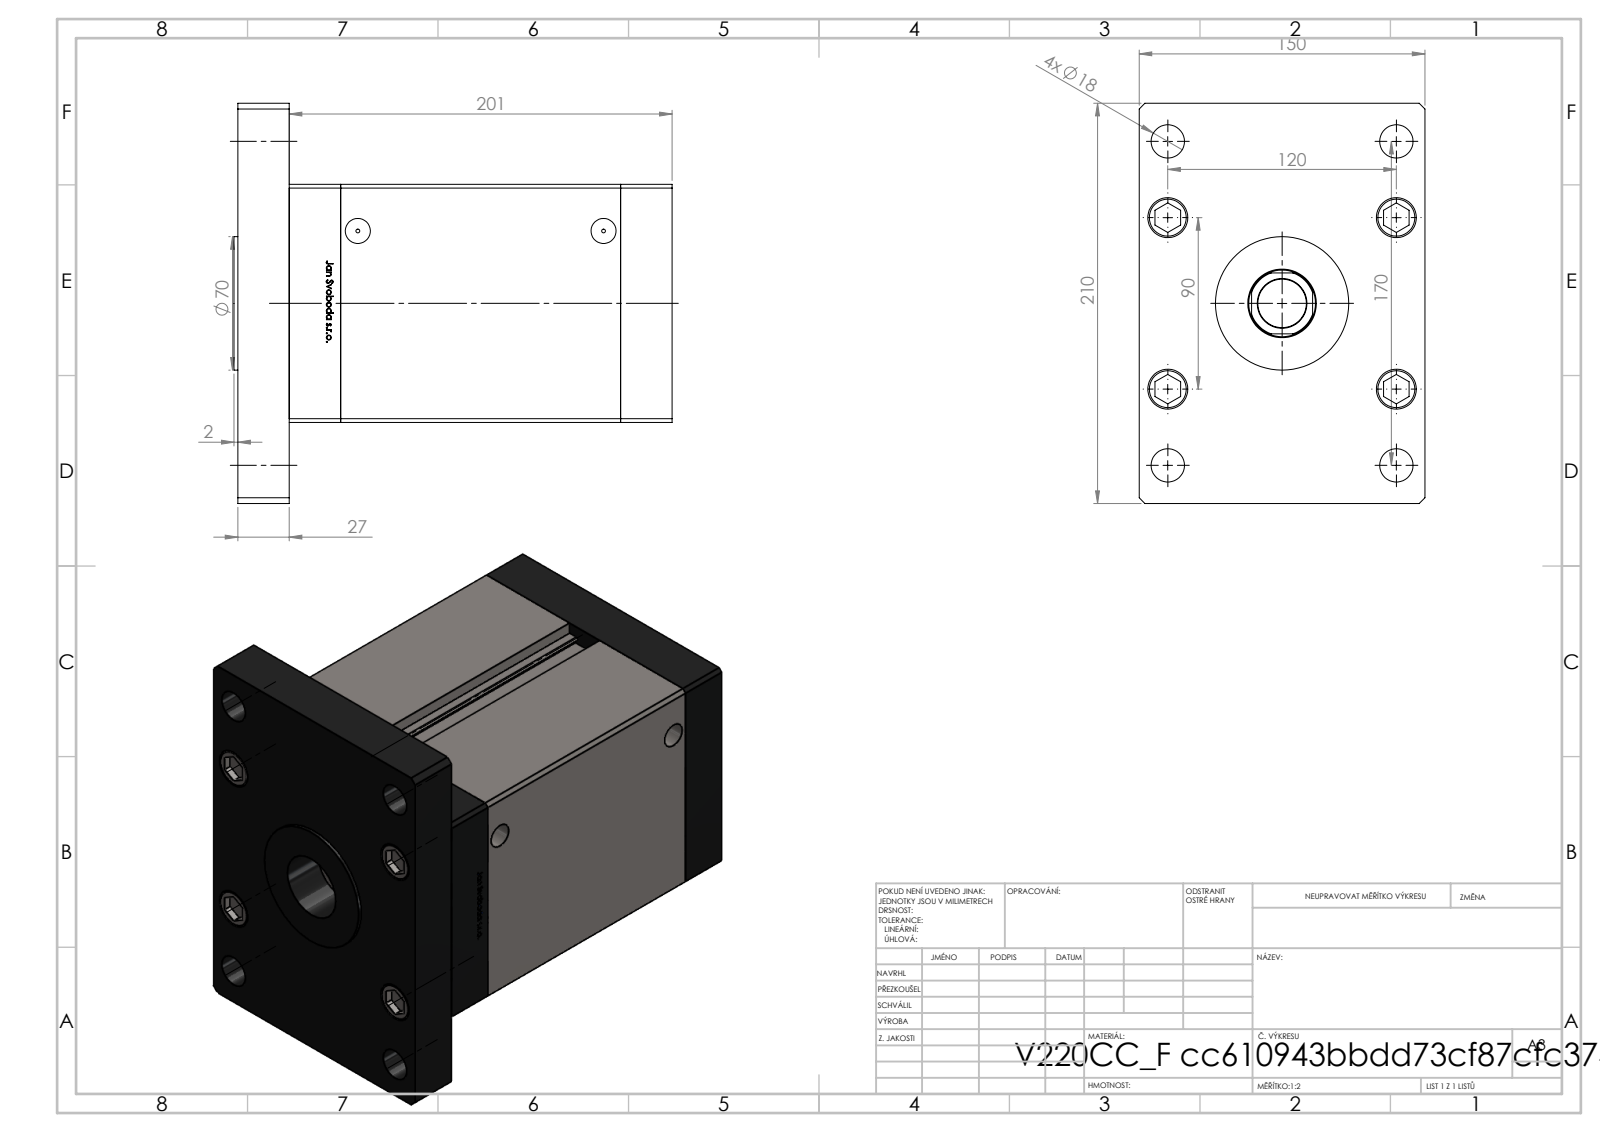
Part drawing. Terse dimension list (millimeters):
name: V220C_VC_F; V220C BACK_F; ALLEN BOLT; V220C_F (+2 more)
written by: SolidWorks 2019 (CONFIG_CONTROL_DESIGN)
unit: mm
bodies: 19 solids, 1308 faces (515 planar, 187 cylindrical, 606 other)
size: 230 × 210 × 150
volume: 3 992 000 mm³; area: 445 989 mm²
holes: 9× ⌀17.5, 5× ⌀22, 4× ⌀16, 4× ⌀21, 2× ⌀2, 2× ⌀13.16, 1× ⌀25.5, 1× ⌀36, 1× ⌀37.5
bosses: 9× ⌀8, 5× ⌀21, 1× ⌀80, 1× ⌀70
rounds: 2× R0.93, 1× R17.5
face distances: 27, 174, 201, 150, 125, 147, 54, 228, 34.8, 7.8
hole spacings: 51, 40, 75, 104.04, 120, 126.49, 130, 176.92
